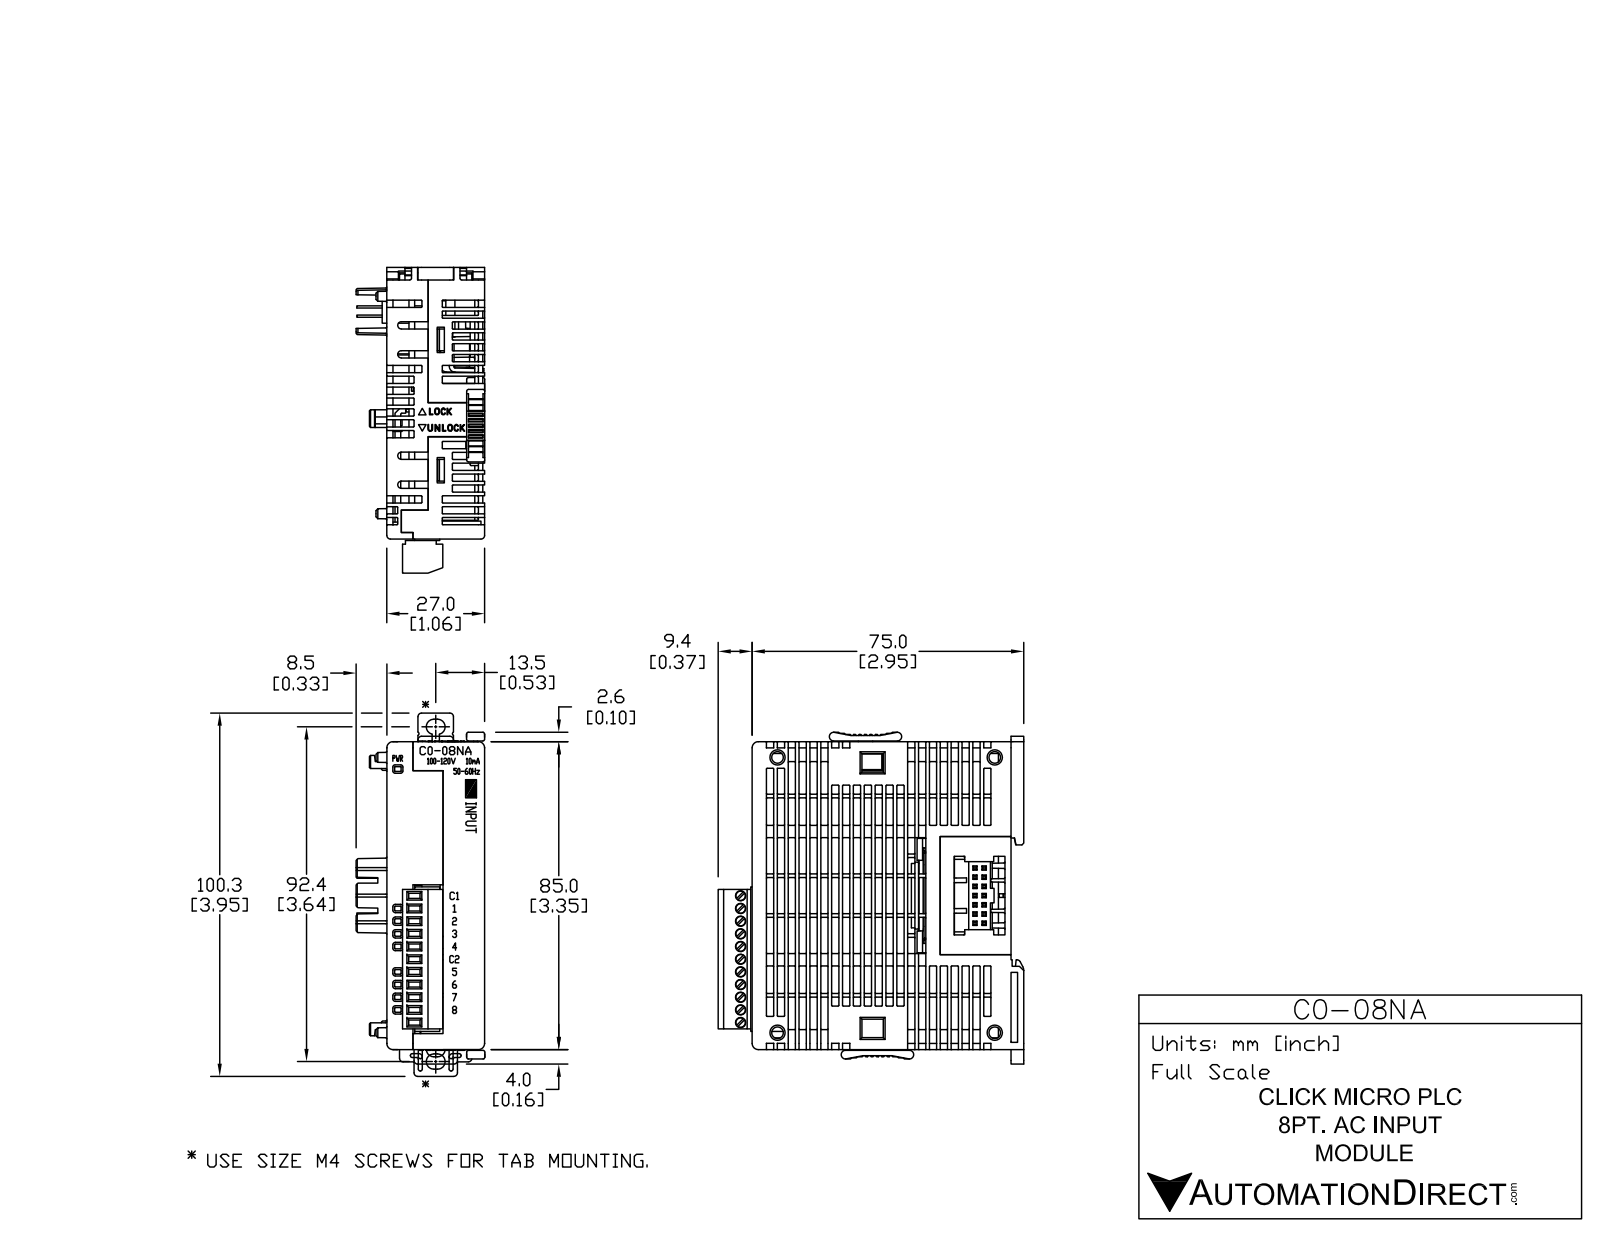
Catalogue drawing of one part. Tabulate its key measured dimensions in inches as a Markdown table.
| quantity | value |
| --- | --- |
| part name | C0-08NA |
| STEP written by | SolidWorks 2009 (AUTOMOTIVE_DESIGN) |
| units | inches |
| bodies | 1 solid, 3689 faces (2637 planar, 968 cylindrical, 84 other) |
| overall size | 3.606 × 3.323 × 1.4 |
| volume | 9.917 in³ |
| surface area | 49.24 in² |
| round holes (diameter × count) | 0.039 × 11, 0.11 × 11, 0.126 × 4, 0.079 × 2 |
| round bosses / shafts (diameter × count) | 0.102 × 11, 0.075 × 1 |
| partial cylindrical surfaces (radius × count) | 0.008 × 570, 0.02 × 43, 0.012 × 22, 0.039 × 18, 0.047 × 12, 0.11 × 11, 0.067 × 6, 0.083 × 4 |
| main face-to-face distances | 1.063, 0.02, 0.02, 1.043, 2.815, 0.067, 3.346, 1.035, 1.056, 3.327 |
| hole center spacings | 0.138, 0.276, 0.413, 0.551, 0.689, 0.827, 0.965, 1.102 |
